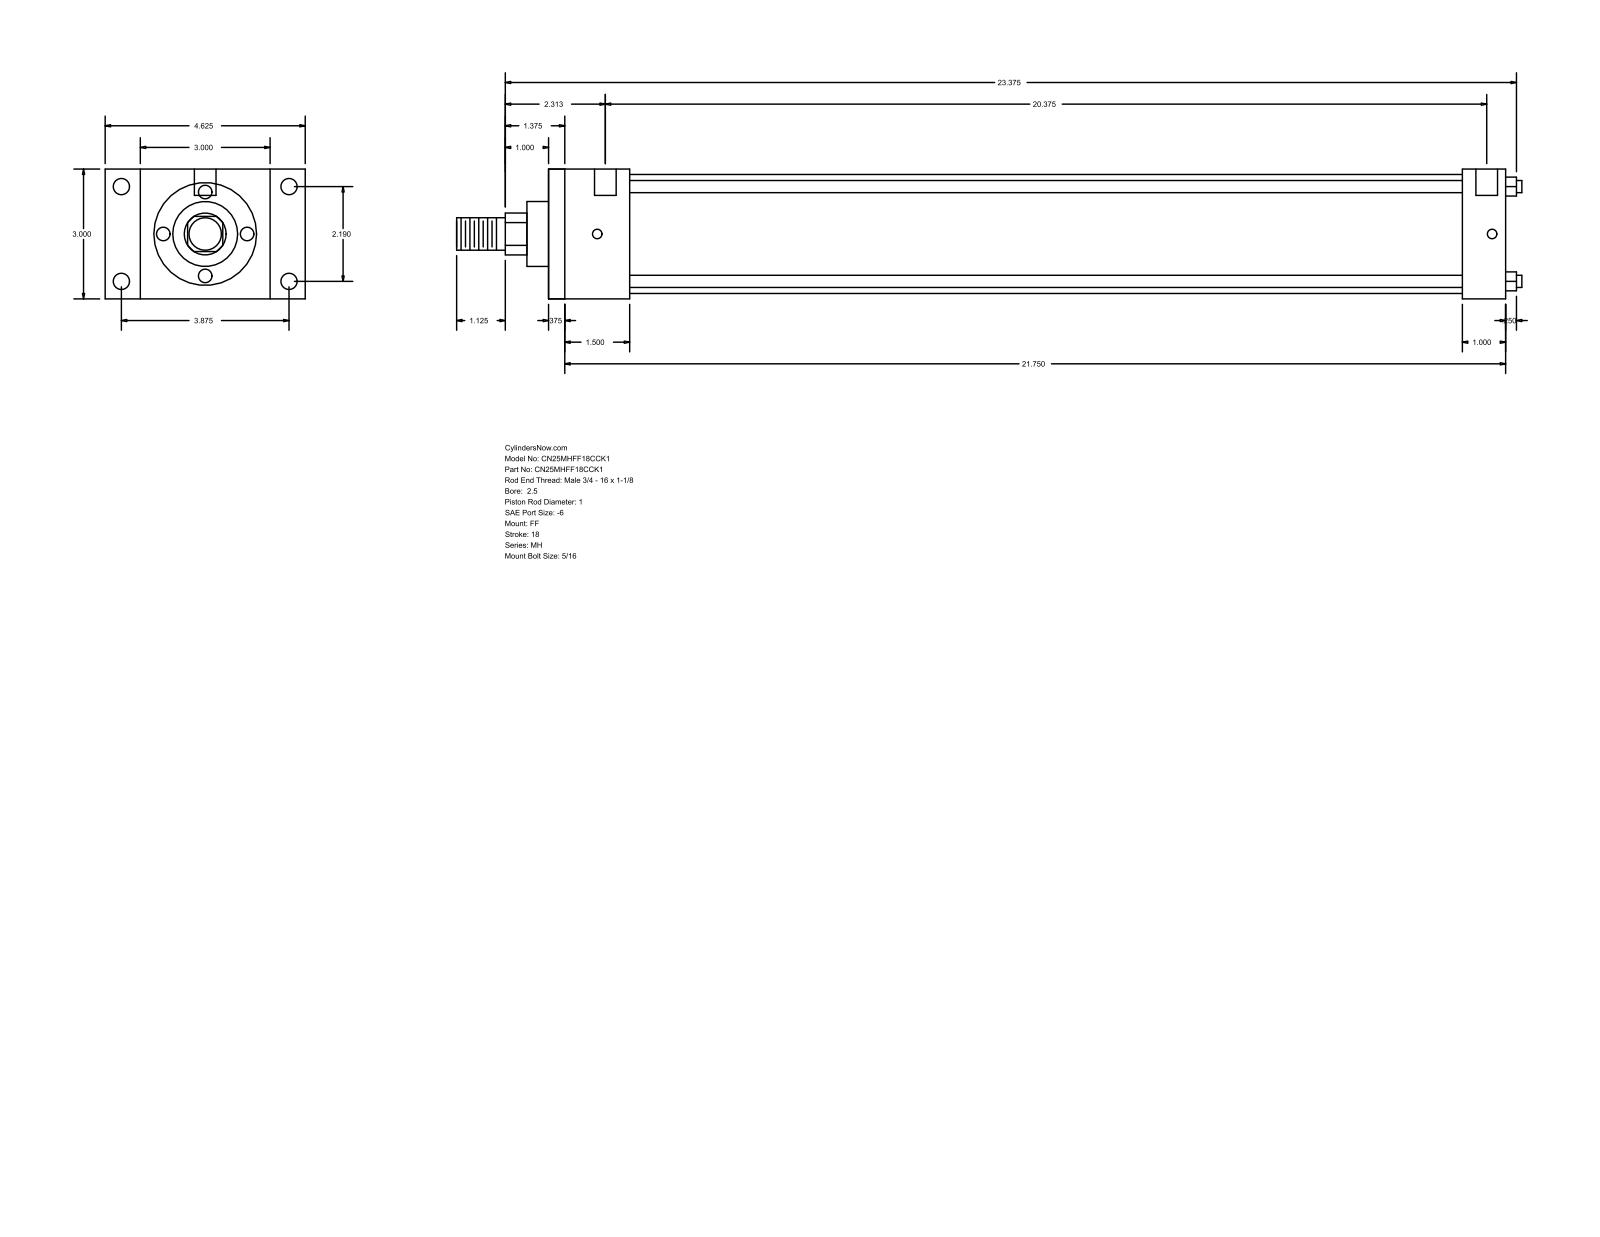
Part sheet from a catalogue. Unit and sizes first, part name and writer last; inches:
Units: inches
Overall size (bounding box): 24.625 × 4.625 × 3
Round holes (diameter × count): ⌀0.219 ×4, ⌀0.375 ×4, ⌀0.5 ×2
Round bosses / shafts (diameter × count): ⌀0.281 ×4, ⌀2.75 ×1, ⌀1.5 ×1, ⌀1 ×1, ⌀0.75 ×1
Partial cylindrical surfaces — rounded edges, fillets, slot ends (radius × count): R0.484 ×1
Main face-to-face distances: 3, 22.125, 0.375, 21.75, 1, 1.875, 21.125, 1.5, 20.75, 19.25
Hole centre spacings: 2.19, 3.875, 4.451, 20.687, 0.125, 0.187, 20.375, 20.5
Bodies: 0 solids, 92 faces (64 planar, 28 cylindrical, 0 other)
Part name (STEP PRODUCT): MH_FF__0250_1
STEP written by: GSSL Pune (CONFIG_CONTROL_DESIGN)
